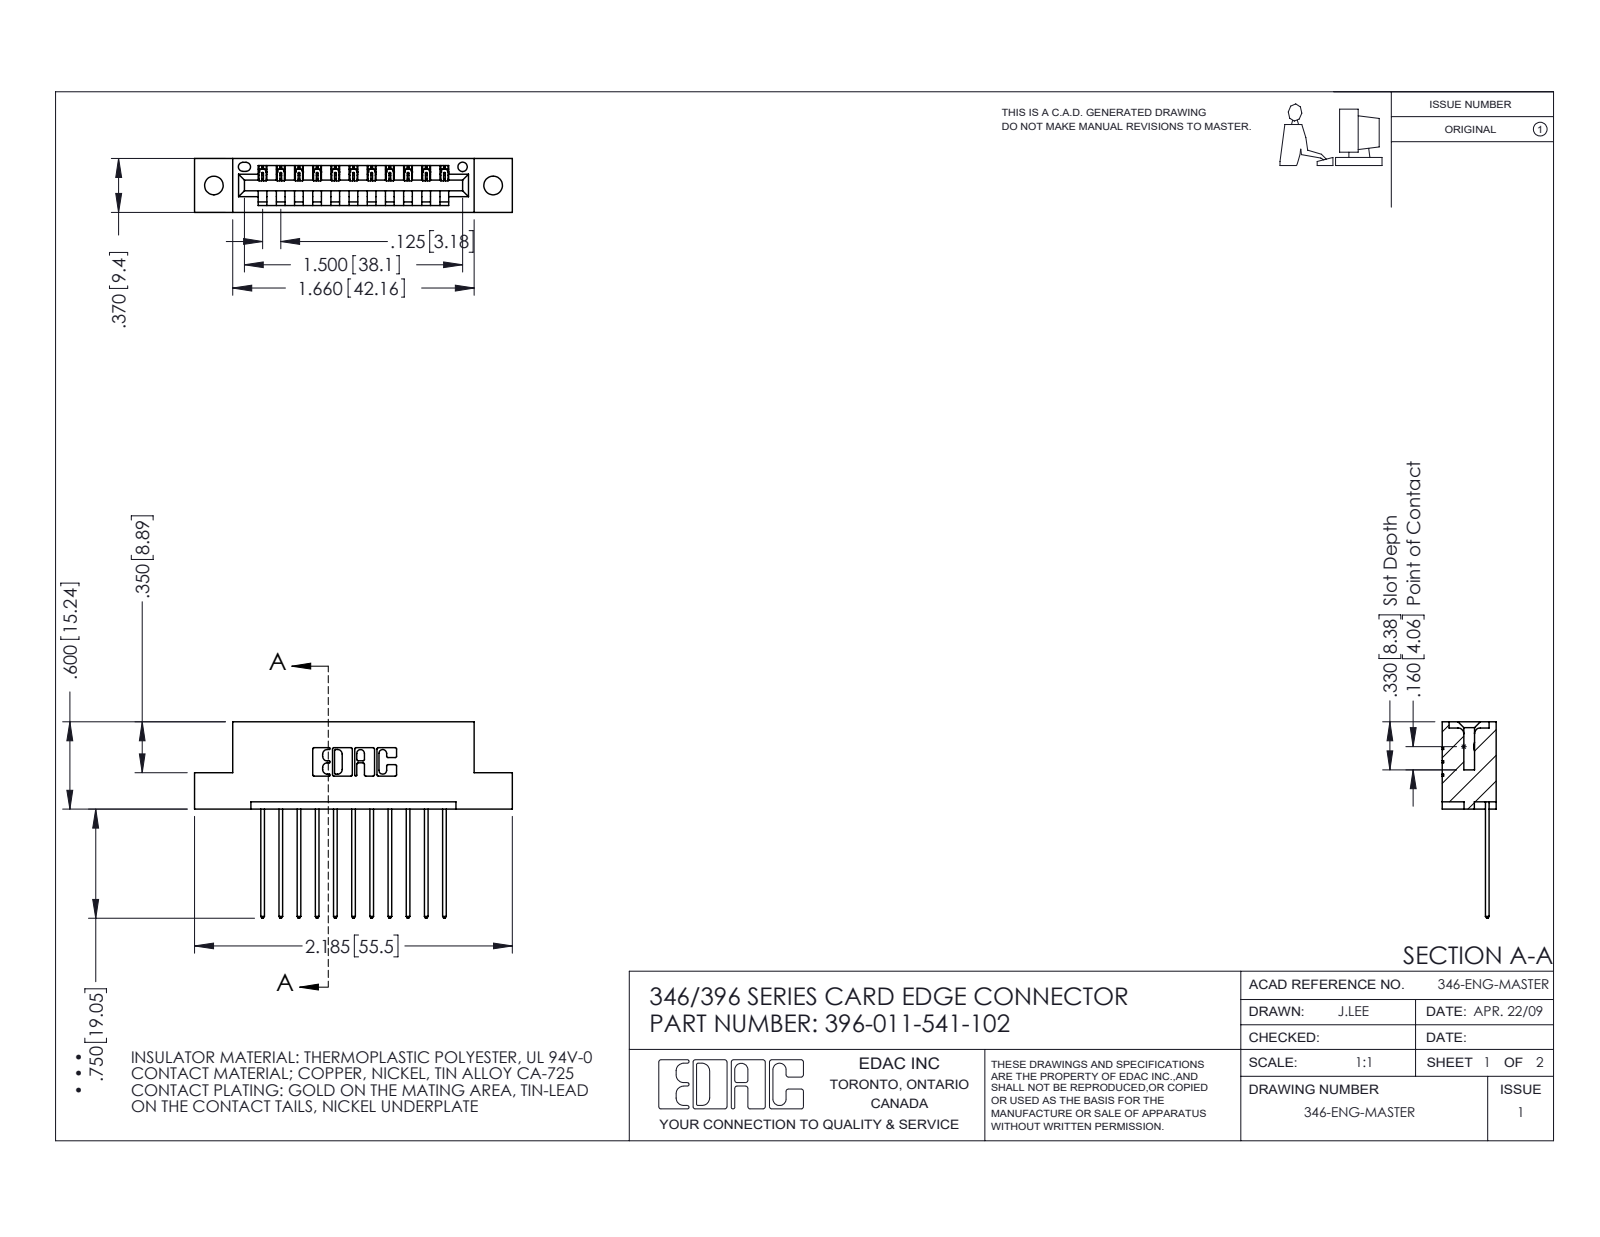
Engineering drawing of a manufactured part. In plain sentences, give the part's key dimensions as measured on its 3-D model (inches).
The part is named "396-011-541-102; 346 Part_Flush Mounting Lugs - 0.128 Dia; 345-292-001_345-293-141". Its 3-D file was written by "SolidWorks 2016 (CONFIG_CONTROL_DESIGN)". It is 12 solids with 760 faces: 516 planar, 244 cylindrical and 0 other. Overall it measures 2.185 by 1.35 by 0.37 inches. Its volume is 0.311 cubic inches and its surface area 9.275 square inches. Round holes: 2 of diameter 0.128, 1 of diameter 0.064. Partial cylindrical surfaces (rounded edges, fillets, slot ends): 22 of radius 0.006, 22 of radius 0.01, 22 of radius 0.01, 6 of radius 0.007, 6 of radius 0.031, 3 of radius 0.026, 2 of radius 0.031, 2 of radius 0.04. The main face-to-face distances are 0.25, 0.048, 0.322, 0.37, 0.072, 0.298, 0.025, 0.148, 0.222, 0.1. The hole center spacings are 0.246, 1.715, 1.92.
